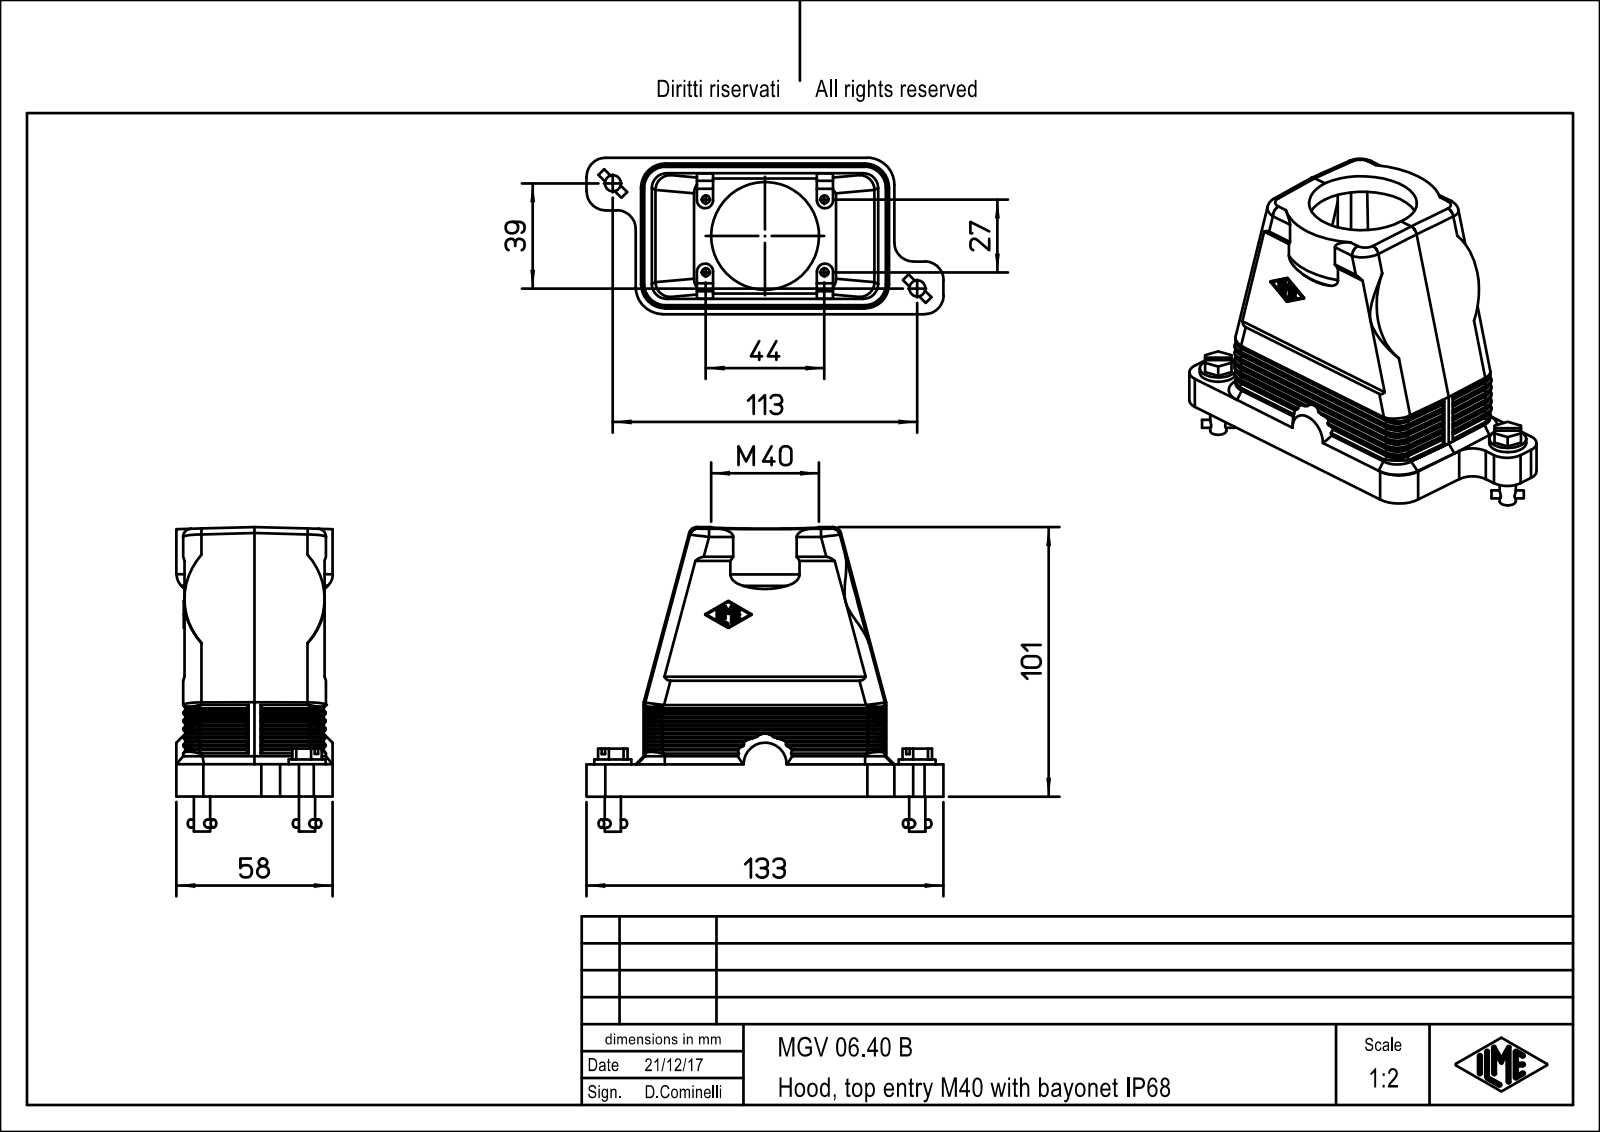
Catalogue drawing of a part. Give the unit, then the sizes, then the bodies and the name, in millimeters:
Units: millimetres
Overall size (bounding box): 132.5 × 113 × 58
Round holes (diameter × count): ⌀3 ×4, ⌀40 ×1
Round bosses / shafts (diameter × count): ⌀13.7 ×2, ⌀6 ×2, ⌀3 ×2
Partial cylindrical surfaces — rounded edges, fillets, slot ends (radius × count): R7 ×62, R0.33 ×15, R5.5 ×8, R3 ×4, R8.5 ×4, R0.17 ×3, R10 ×2, R0.67 ×1
Main face-to-face distances: 6, 44.5, 3, 55, 52, 2.5, 3.33, 0.5, 55.5, 52.5
Hole centre spacings: 25.81, 27, 44, 51.62
Volume: 125 976 mm³ · Surface area: 63 104 mm²
Bodies: 1 solid, 544 faces (260 planar, 135 cylindrical, 149 other)
Part name (STEP PRODUCT): MGV_06.40_B
STEP written by: PTC Creo Elements/Direct Modeling 19.0E 27-Jun-2016 (C) Parametric Technology GmbH (AUTOMOTIVE_DESIGN)
